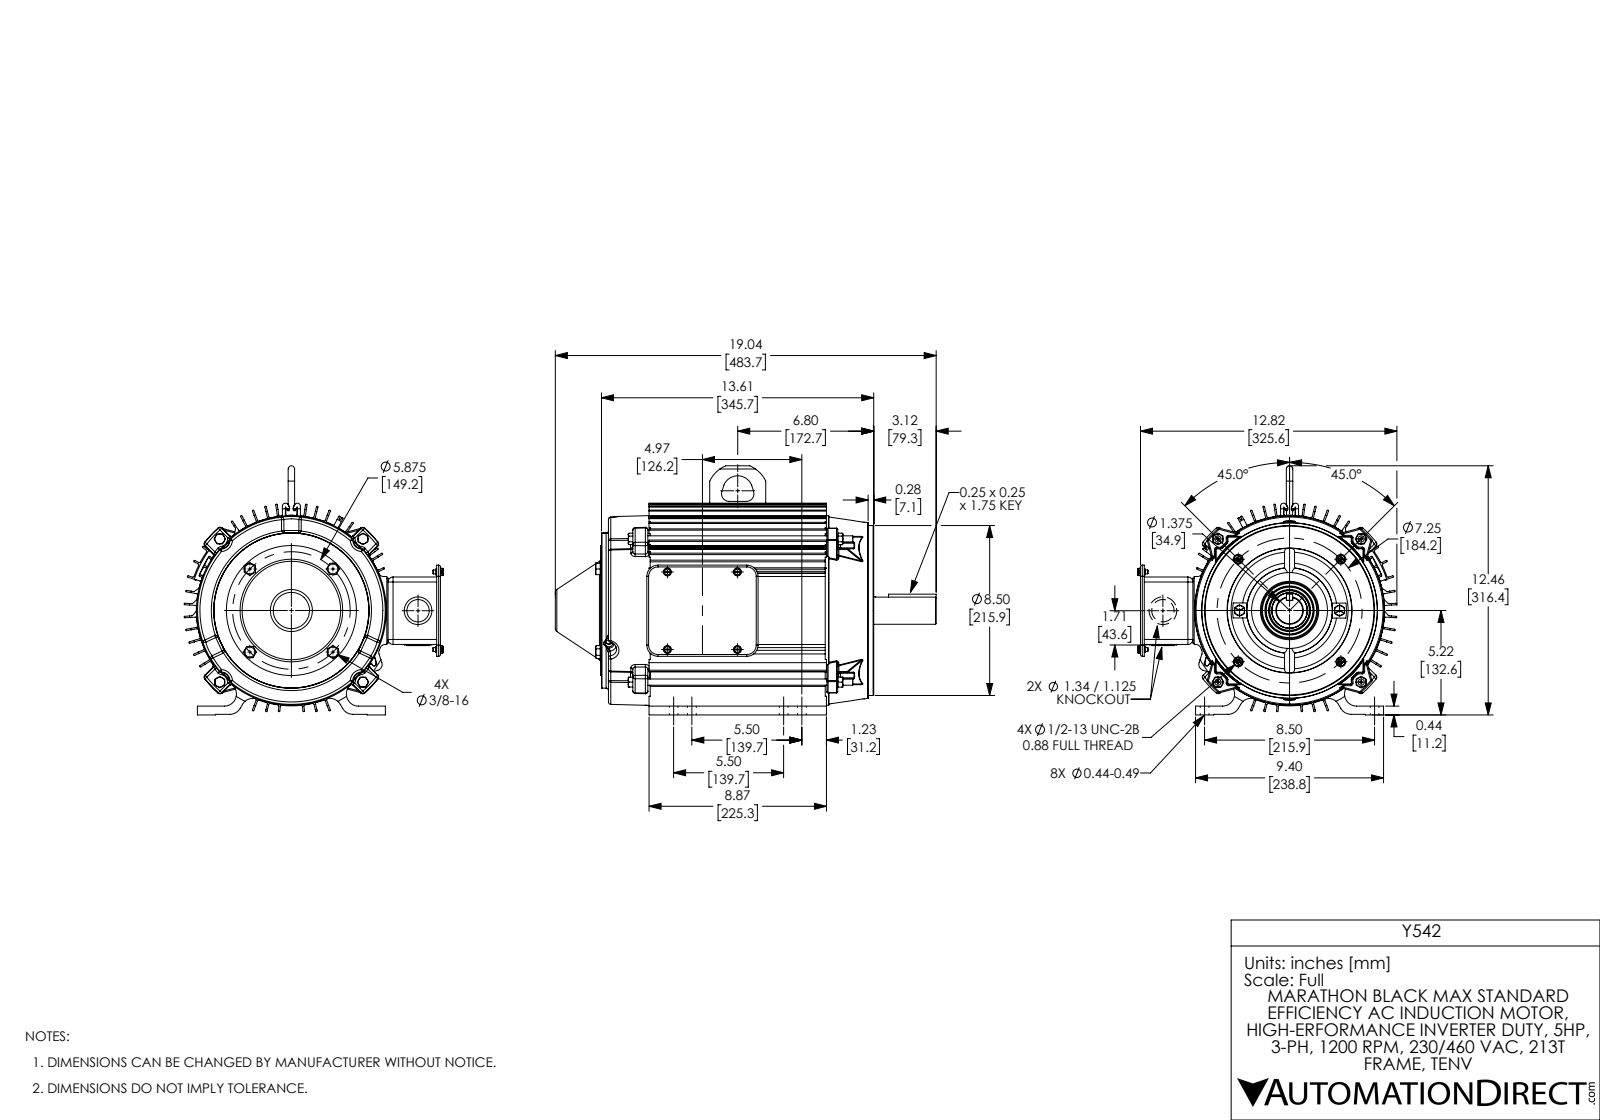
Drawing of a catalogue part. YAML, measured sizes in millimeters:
part_name: "SS330216-875_RevD r1"
step_written_by: "SolidWorks 2017 (AUTOMOTIVE_DESIGN)"
units: millimeters
bodies: {solids: 31, faces: 3674, planar: 1000, cylindrical: 1029, other: 1645}
overall_size: [483.7, 329.1, 316.4]
volume: 3787000
surface_area: 1472000
round_holes:
  - {diameter: 11.1, count: 8}
  - {diameter: 8.7, count: 6}
  - {diameter: 4.4, count: 4}
  - {diameter: 5.6, count: 4}
  - {diameter: 6.5, count: 4}
  - {diameter: 7.9, count: 4}
  - {diameter: 7.9, count: 4}
  - {diameter: 10.3, count: 4}
  - {diameter: 10.7, count: 4}
  - {diameter: 4.4, count: 2}
  - {diameter: 4.4, count: 2}
  - {diameter: 6.4, count: 2}
round_bosses_or_shafts:
  - {diameter: 7.9, count: 6}
  - {diameter: 12.7, count: 4}
  - {diameter: 10.1, count: 4}
  - {diameter: 9.5, count: 4}
  - {diameter: 7.5, count: 4}
  - {diameter: 4.8, count: 4}
  - {diameter: 11.2, count: 2}
  - {diameter: 235.5, count: 1}
partial_cylinders:
  - {radius: 1.5, count: 162}
  - {radius: 3, count: 130}
  - {radius: 1, count: 32}
  - {radius: 6.4, count: 25}
  - {radius: 0.8, count: 19}
  - {radius: 4.8, count: 12}
  - {radius: 2.4, count: 8}
  - {radius: 6.4, count: 8}
face_to_face_distances: [1.9, 1.5, 66.6, 2.5, 69.4, 345.7, 68.1, 65, 4.3, 84.1]
hole_center_spacings: [118.5, 148.7, 158.2, 53.8, 101.6, 17.5, 23.1, 36.5]
